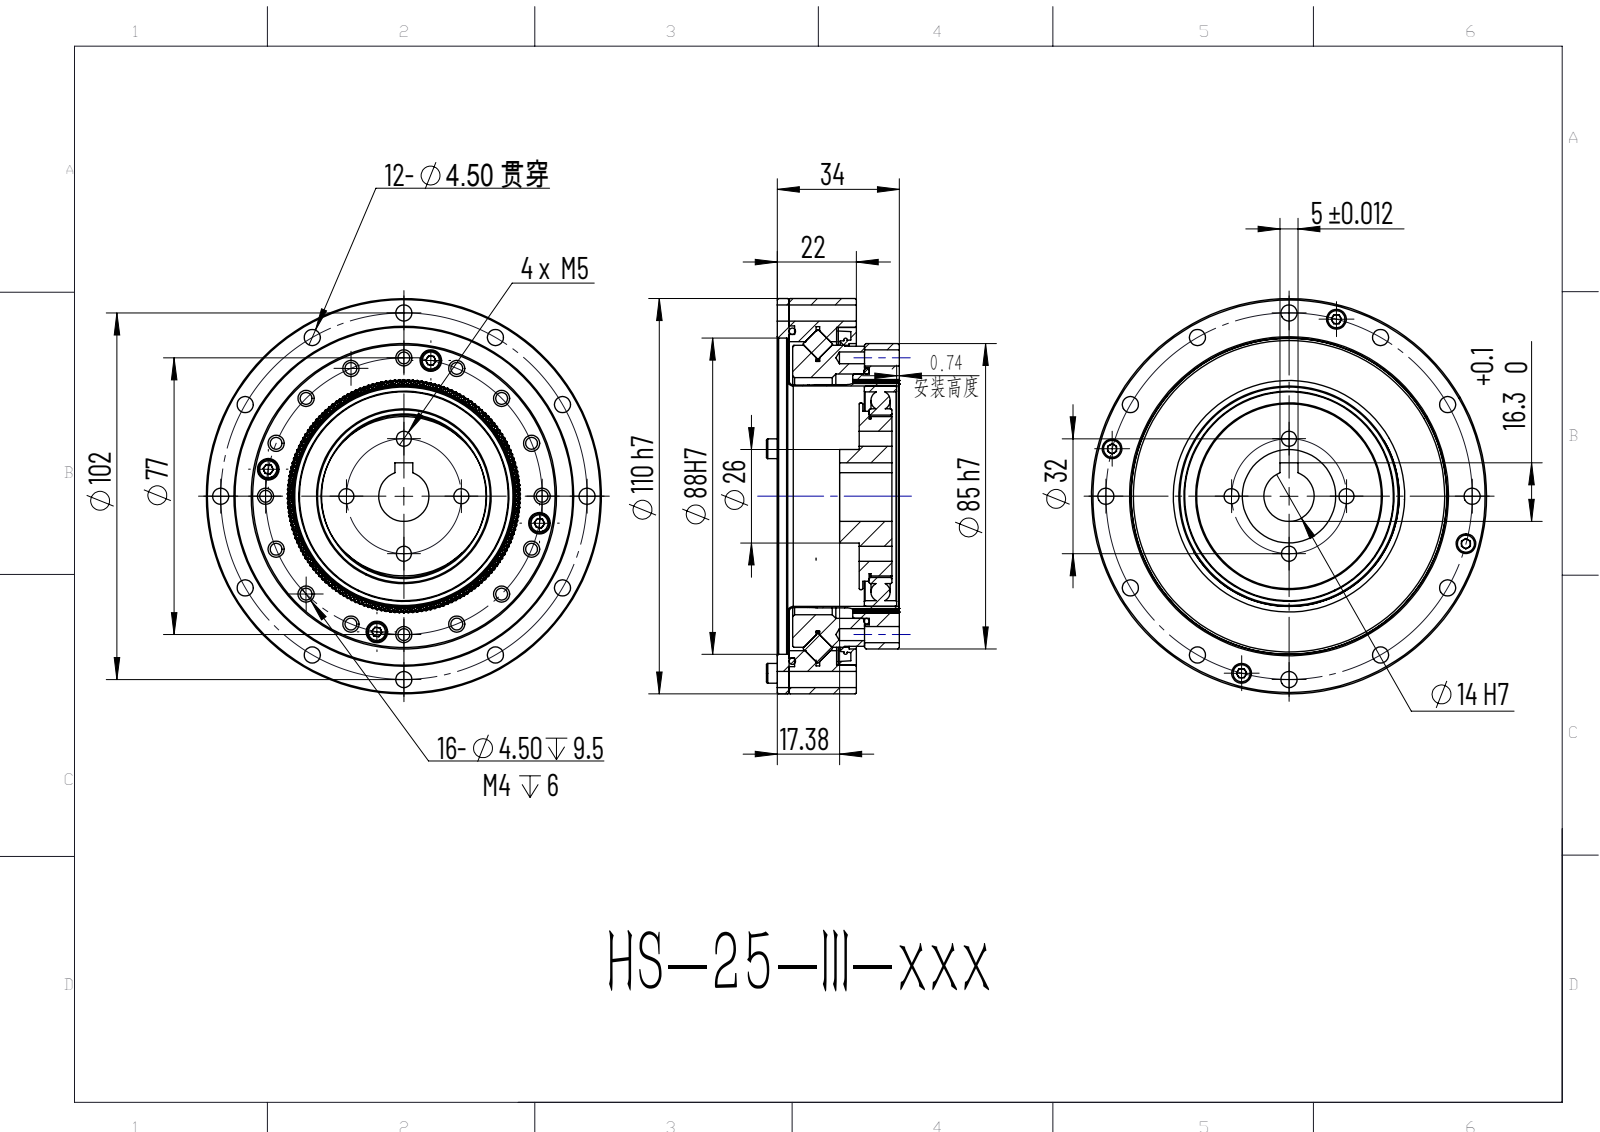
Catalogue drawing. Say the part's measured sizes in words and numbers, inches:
The part is named "HS-25-III; hexagon socket head cap screws gb_GB_FASTENER_SCREWS_HSHCS M3X8-C; ???????-STXB-25080; 25-III???????????_?A?O <1> (+8 more)". Its 3-D file was written by "ONSHAPE BY PTC INC, 1.201 (AP242_MANAGED_MODEL_BASED_3D_ENGINEERING_MIM_LF)". It is 91 solids with 4447 faces: 1119 planar, 2498 cylindrical and 830 other. Overall it measures 4.331 by 4.331 by 1.457 inches. Its volume is 9.866 cubic inches and its surface area 185.2 square inches. Round holes: 28 of diameter 0.177, 16 of diameter 0.13, 8 of diameter 0.098, 4 of diameter 0.134, 4 of diameter 0.138, 4 of diameter 0.165, 4 of diameter 0.236, 1 of diameter 0.081, 1 of diameter 0.114, 1 of diameter 0.197, 1 of diameter 0.551, 1 of diameter 1.78. Round bosses or shafts: 36 of diameter 0.236, 8 of diameter 0.217, 8 of diameter 0.118, 1 of diameter 4.331, 1 of diameter 3.543, 1 of diameter 3.307, 1 of diameter 3.287, 1 of diameter 2.953. Partial cylindrical surfaces (rounded edges, fillets, slot ends): 324 of radius 0.016, 324 of radius 0.023, 320 of radius 0.009, 320 of radius 0.015, 320 of radius 0.024, 162 of radius 0.006, 36 of radius 0.119, 1 of radius 1.235. The main face-to-face distances are 0.13, 0.091, 0.736, 0.827, 0.039, 0.866, 0.059, 0.957, 0.472, 0.115. The hole center spacings are 2.008, 1.039, 3.478, 3.879, 0.524, 0.591, 1.028, 1.496.
